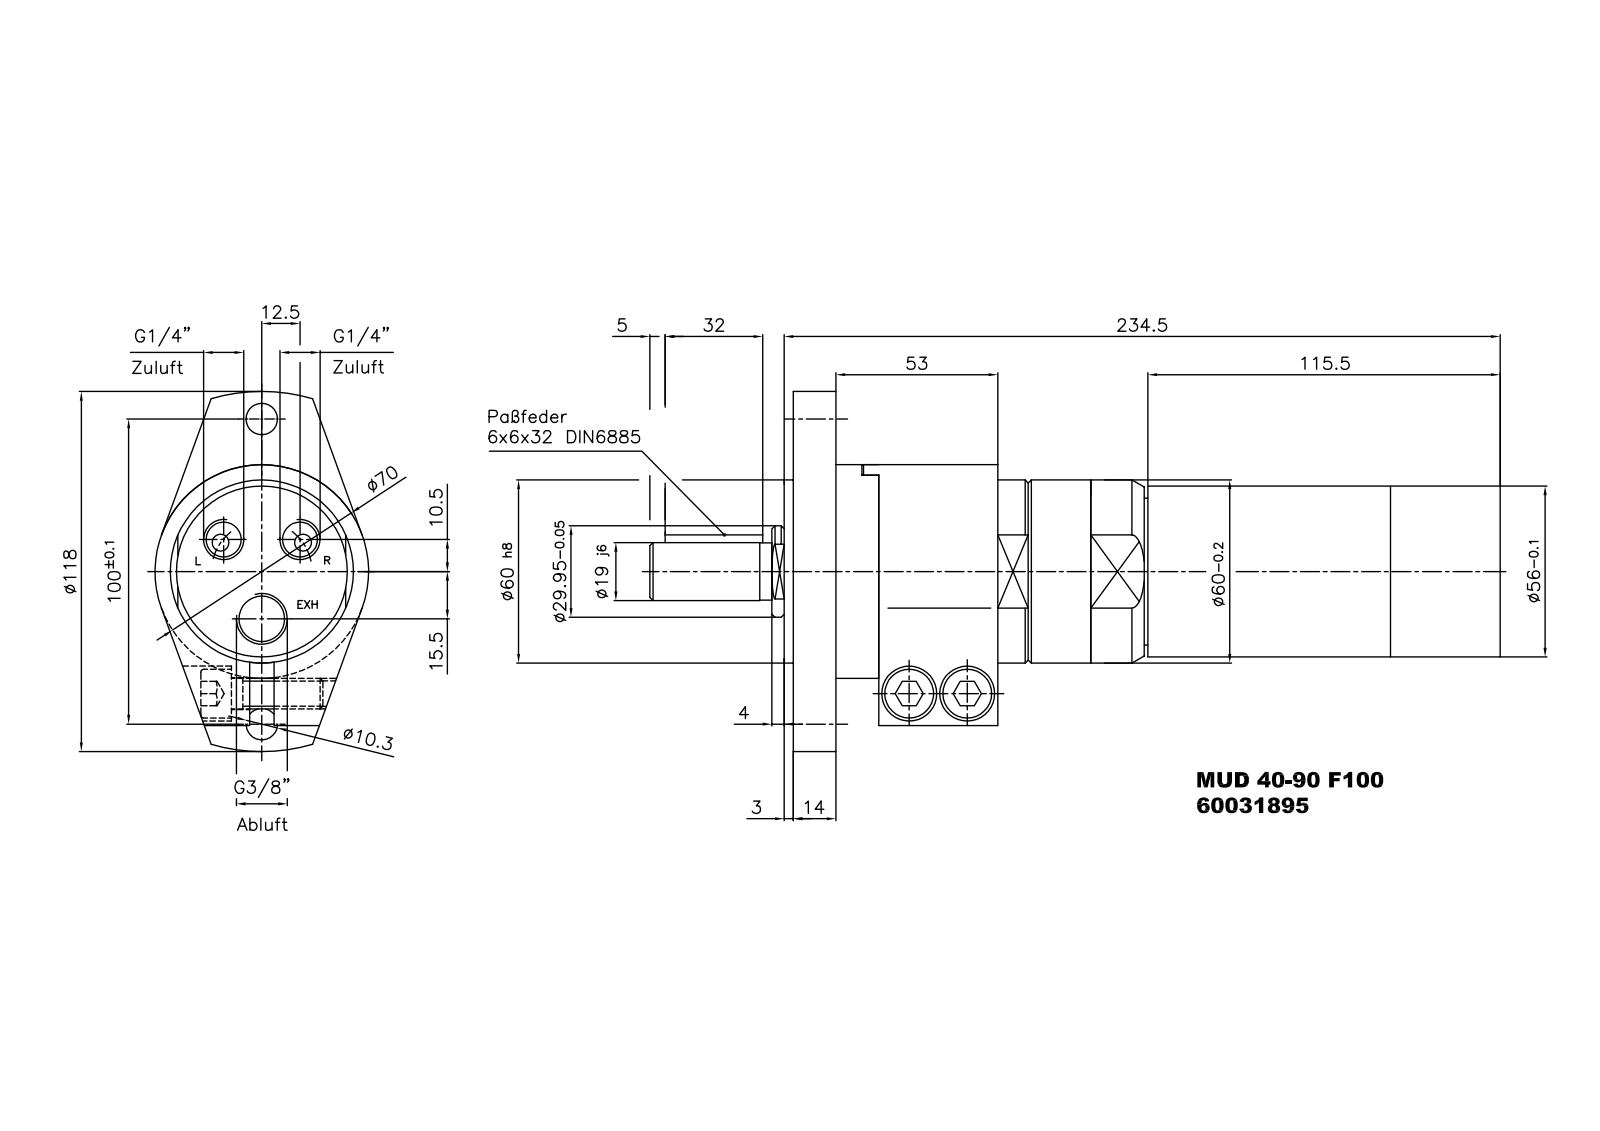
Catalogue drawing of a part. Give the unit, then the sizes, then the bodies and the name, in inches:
Units: inches
Overall size (bounding box): 10.972 × 4.646 × 2.756
Round holes (diameter × count): ⌀0.33 ×2, ⌀0.406 ×2, ⌀0.413 ×2, ⌀0.451 ×2, ⌀0.709 ×2, ⌀0.061 ×1, ⌀0.063 ×1, ⌀0.157 ×1, ⌀0.217 ×1, ⌀0.589 ×1, ⌀0.745 ×1, ⌀1.378 ×1
Round bosses / shafts (diameter × count): ⌀0.63 ×2, ⌀0.394 ×2, ⌀2.756 ×1, ⌀2.362 ×1, ⌀2.205 ×1, ⌀2.172 ×1, ⌀1.897 ×1, ⌀1.179 ×1
Partial cylindrical surfaces — rounded edges, fillets, slot ends (radius × count): R0.118 ×2, R1.074 ×1, R2.323 ×1
Main face-to-face distances: 0.551, 9.122, 8.571, 0.669, 0.118, 9.24, 2.76, 2.642, 2.091, 6.48
Hole centre spacings: 0.643, 1.136, 1.631, 1.969, 2.432, 0.61, 0.748, 0.984
Volume: 45.73 in³ · Surface area: 122.9 in²
Bodies: 1 solid, 161 faces (80 planar, 46 cylindrical, 35 other)
Part name (STEP PRODUCT): MUD 40-90 F100_60031895
STEP written by: Autodesk Inventor 2016 (AUTOMOTIVE_DESIGN)
